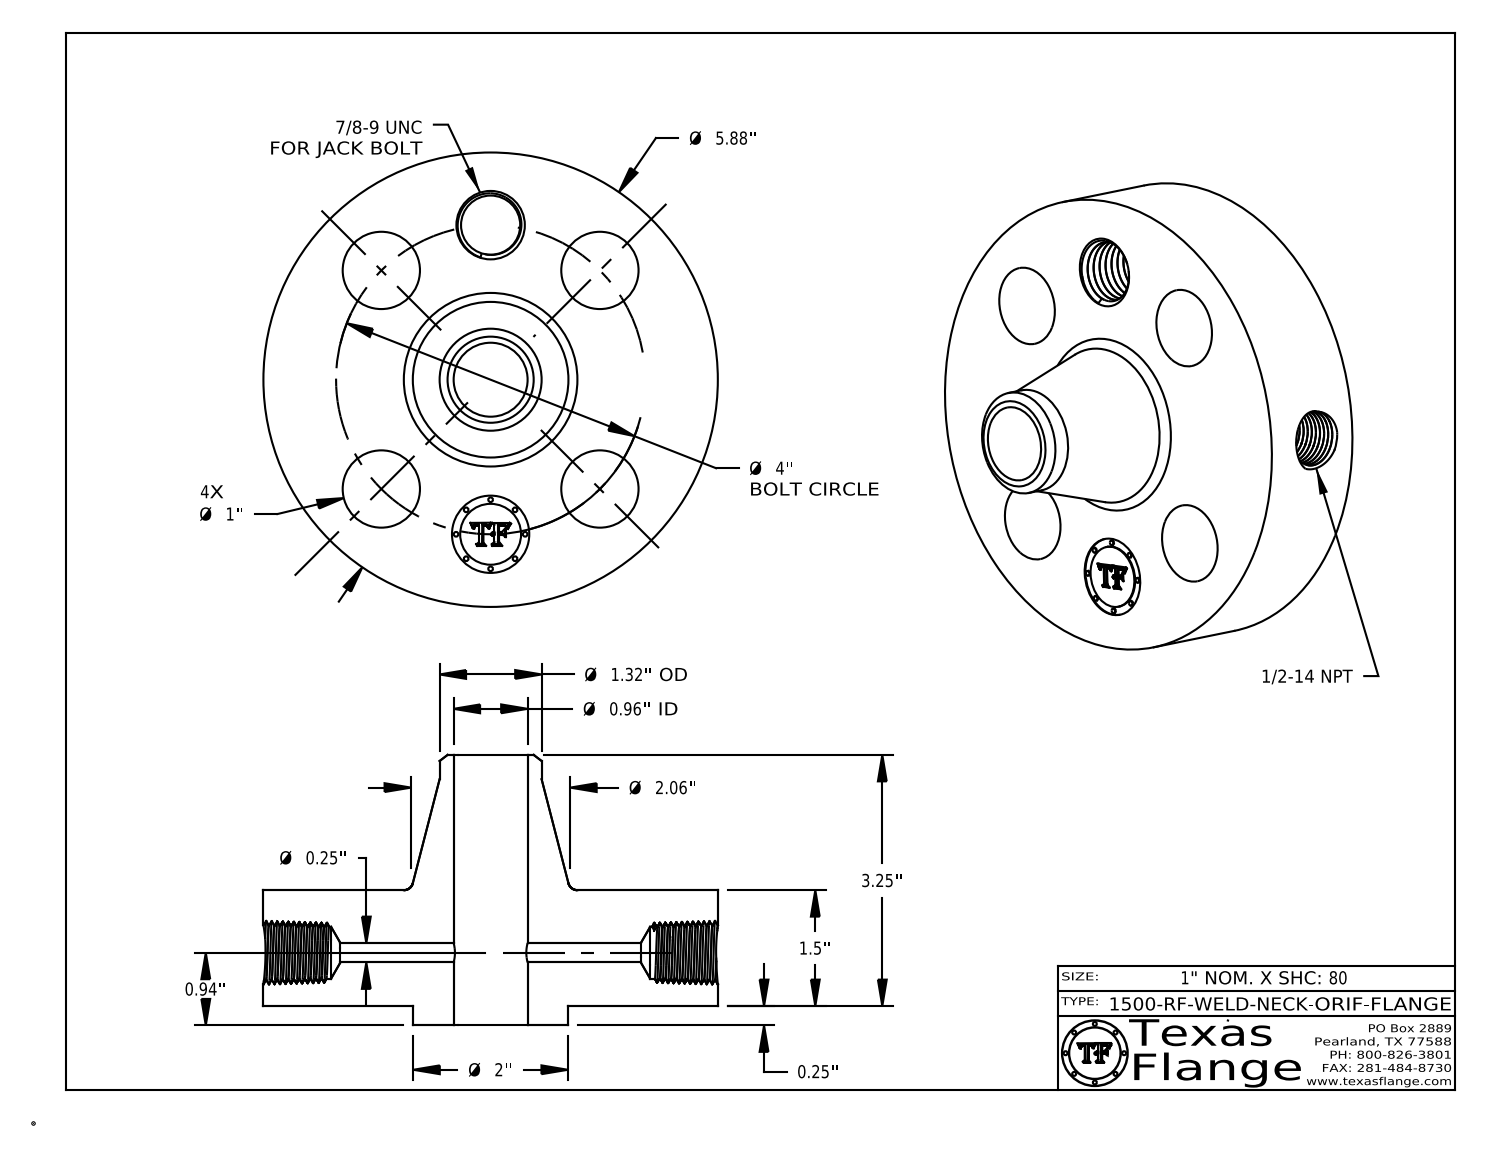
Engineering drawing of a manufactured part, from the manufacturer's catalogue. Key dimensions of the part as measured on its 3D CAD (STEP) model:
Part name (STEP PRODUCT): 1500-RF-WELD-NECK
STEP written by: CATIA V5 STEP AP214 (AUTOMOTIVE_DESIGN)
Units: inches
Bodies: 1 solid, 749 faces (369 planar, 82 cylindrical, 298 other)
Overall size (bounding box): 5.88 × 5.88 × 3.5
Volume: 36.26 in³ · Surface area: 125.7 in²
Round holes (diameter × count): ⌀1 ×5, ⌀0.25 ×1, ⌀0.672 ×1, ⌀0.766 ×1, ⌀0.957 ×1
Round bosses / shafts (diameter × count): ⌀0.061 ×8, ⌀5.88 ×1, ⌀2 ×1, ⌀1.32 ×1, ⌀0.788 ×1
Main face-to-face distances: 1.5, 1.75, 0.25, 1.735, 1.485, 0.015, 3.5, 3.25, 1.765, 0.298
Hole centre spacings: 2, 1.531, 2.828, 3.695, 4
